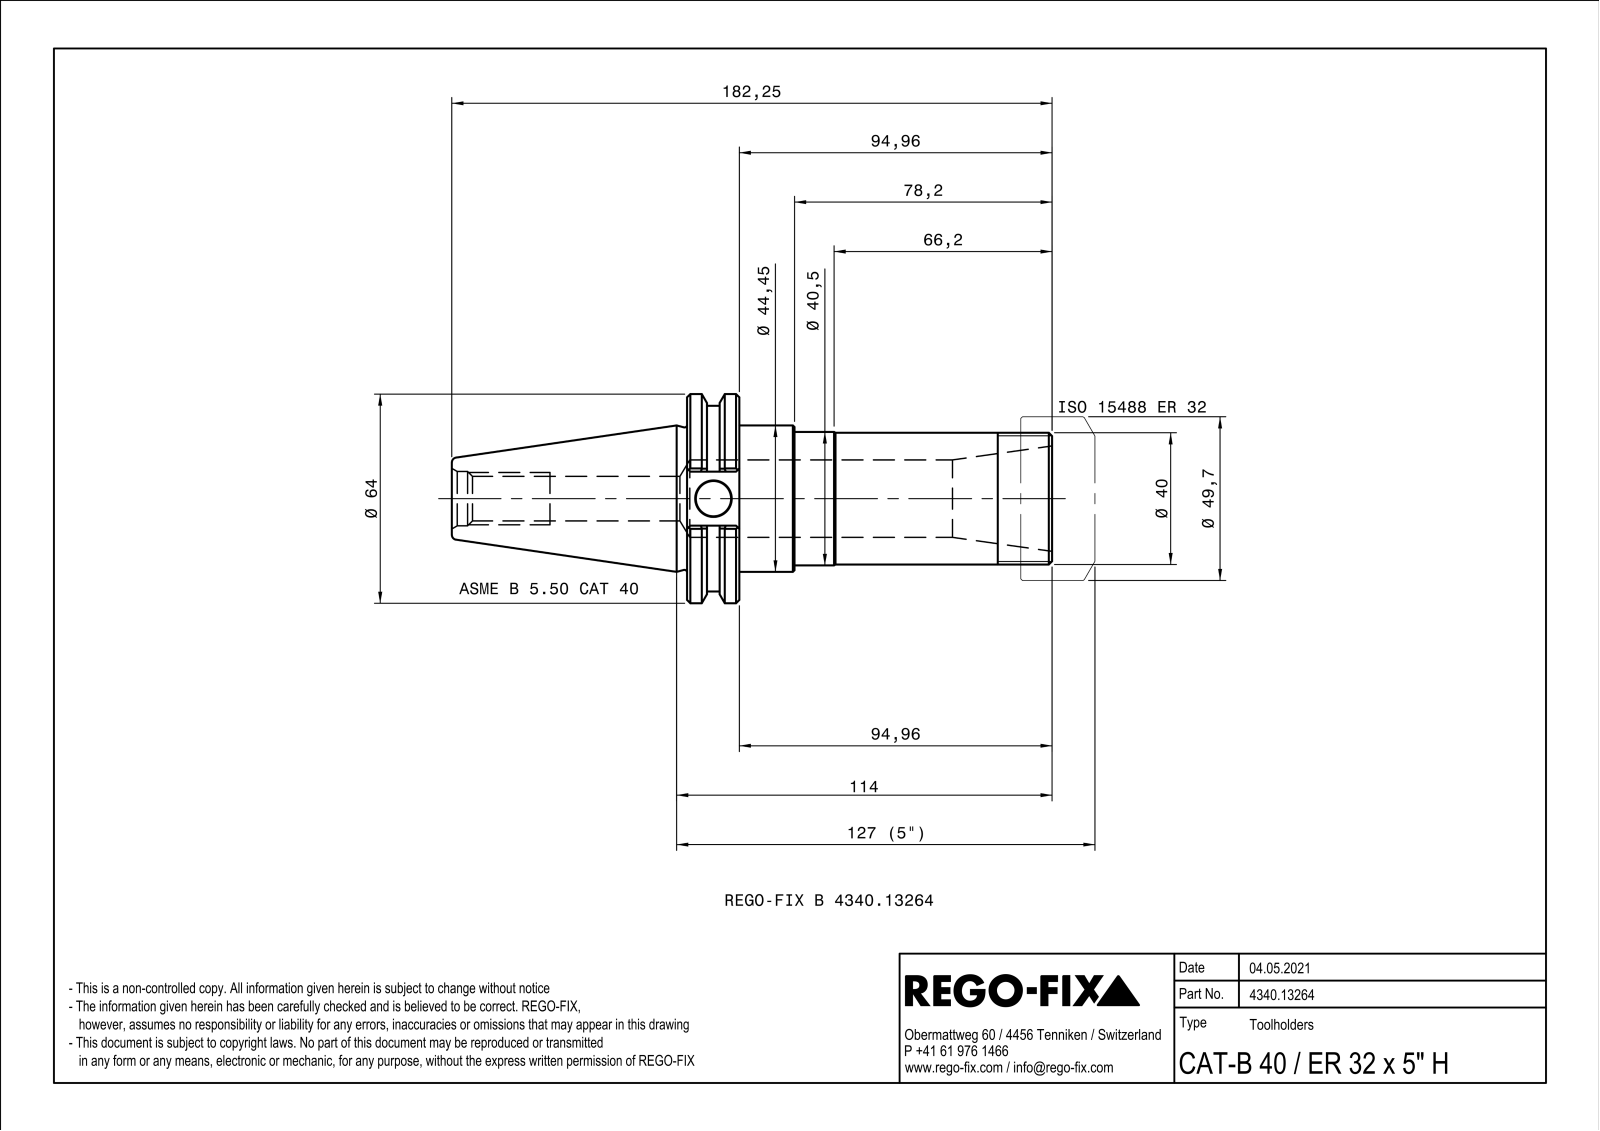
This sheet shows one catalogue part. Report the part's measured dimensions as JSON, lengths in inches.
{"part_name": "NOCUT", "step_written_by": "SIEMENS PLM Software Solid Edge ST10 (AUTOMOTIVE_DESIGN)", "units": "inches", "bodies": {"solids": 1, "faces": 111, "planar": 31, "cylindrical": 32, "other": 48}, "overall_size": [7.175, 2.5, 2.393], "volume_in3": 10.51, "surface_area_in2": 62.47, "round_holes": [[0.128, 2], [0.154, 2], [0.421, 1], [0.533, 1], [0.65, 1], [0.925, 1]], "round_bosses_or_shafts": [[2.5, 1], [2.219, 1], [1.75, 1], [1.594, 1], [1.575, 1]], "partial_cylinders_radius": [[0.02, 4]], "face_to_face_distances": [0.625, 3.739, 4.363, 1.863, 0.645, 7.175, 3.437, 2.812, 3.974, 0.236]}
